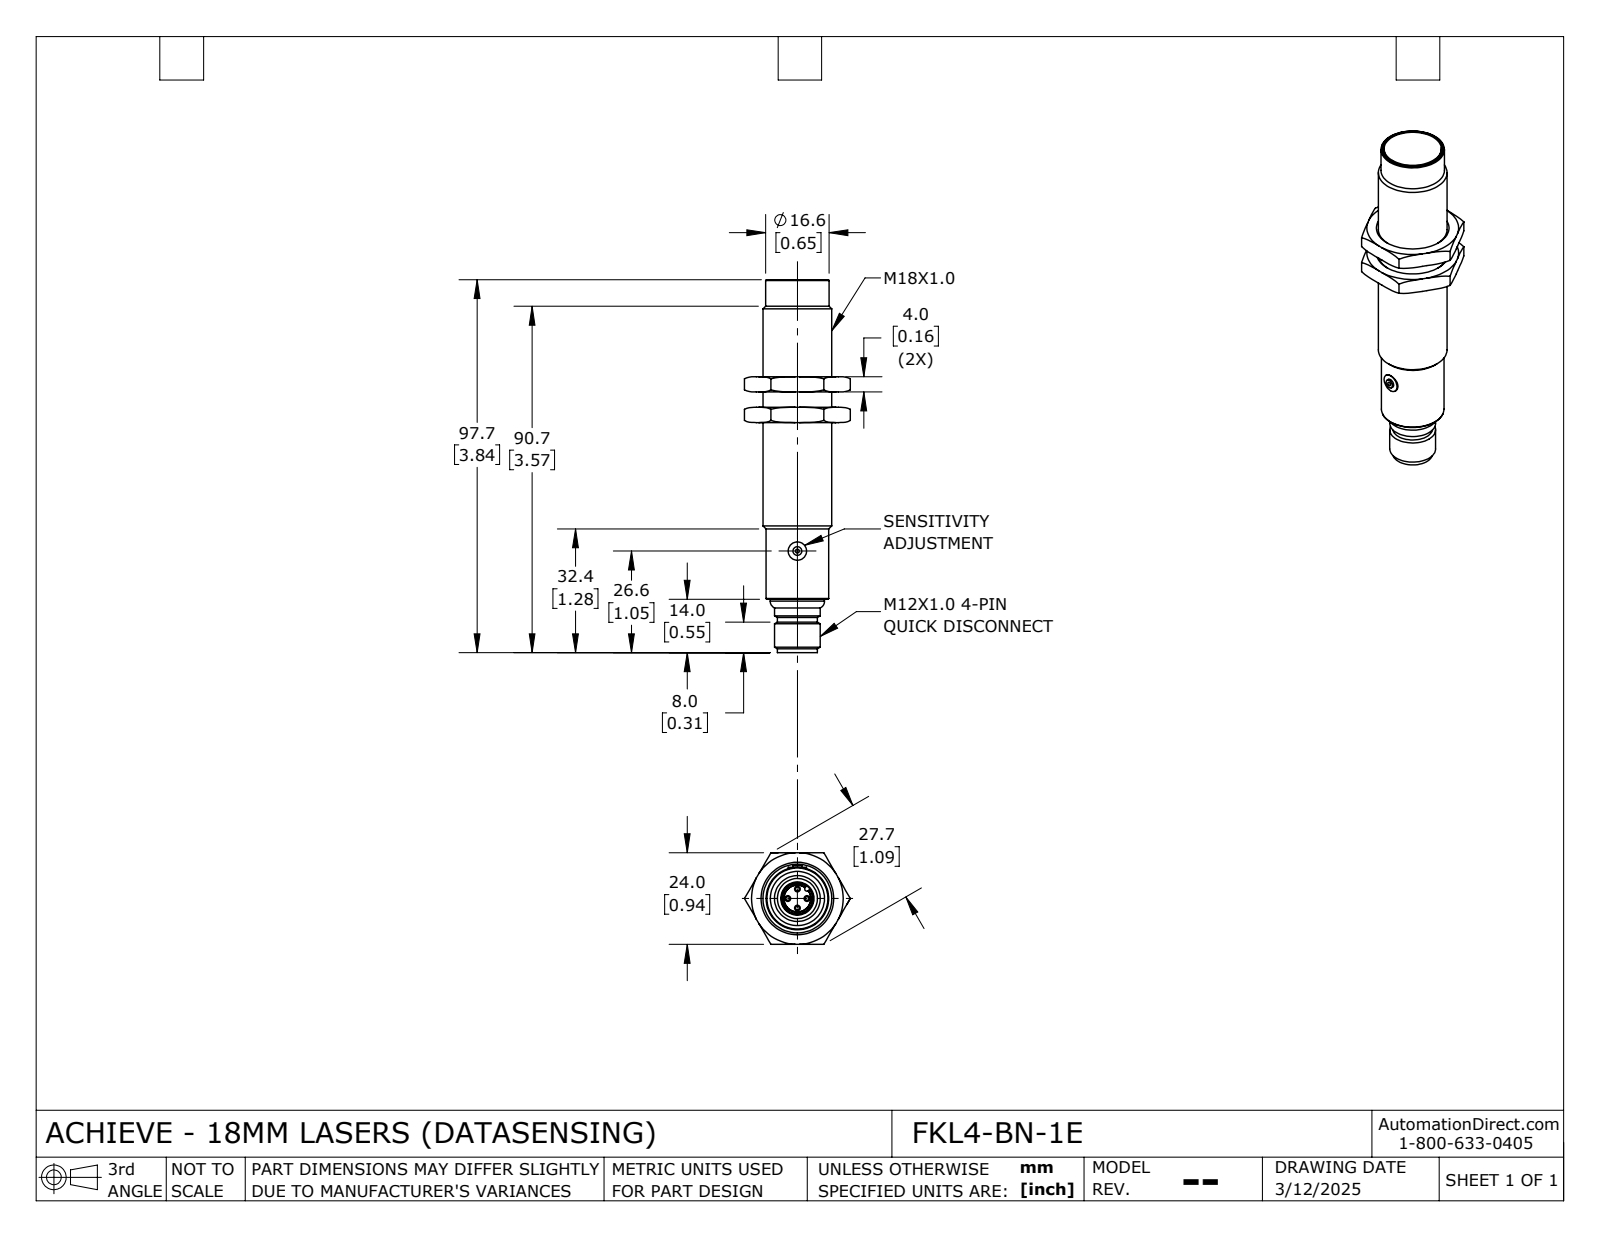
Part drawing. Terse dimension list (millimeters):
name: FKL4-BN-1E_Default
written by: SolidWorks 2024 (CONFIG_CONTROL_DESIGN)
unit: mm
bodies: 3 solids, 121 faces (43 planar, 29 cylindrical, 49 other)
size: 97.6 × 27.7 × 24
volume: 23 010 mm³; area: 9 071 mm²
holes: 1× ⌀4.7, 1× ⌀7.1, 1× ⌀8.3, 1× ⌀14.9, 1× ⌀18
bosses: 4× ⌀1, 1× ⌀16.6, 1× ⌀16.4, 1× ⌀15, 1× ⌀14.8, 1× ⌀14.2, 1× ⌀12, 1× ⌀10.5
rounds: 2× R0.5, 1× R0.6, 1× R7.5
face distances: 4, 8, 24, 2.4, 2.5, 30.9, 31, 33.4, 22.9, 23
